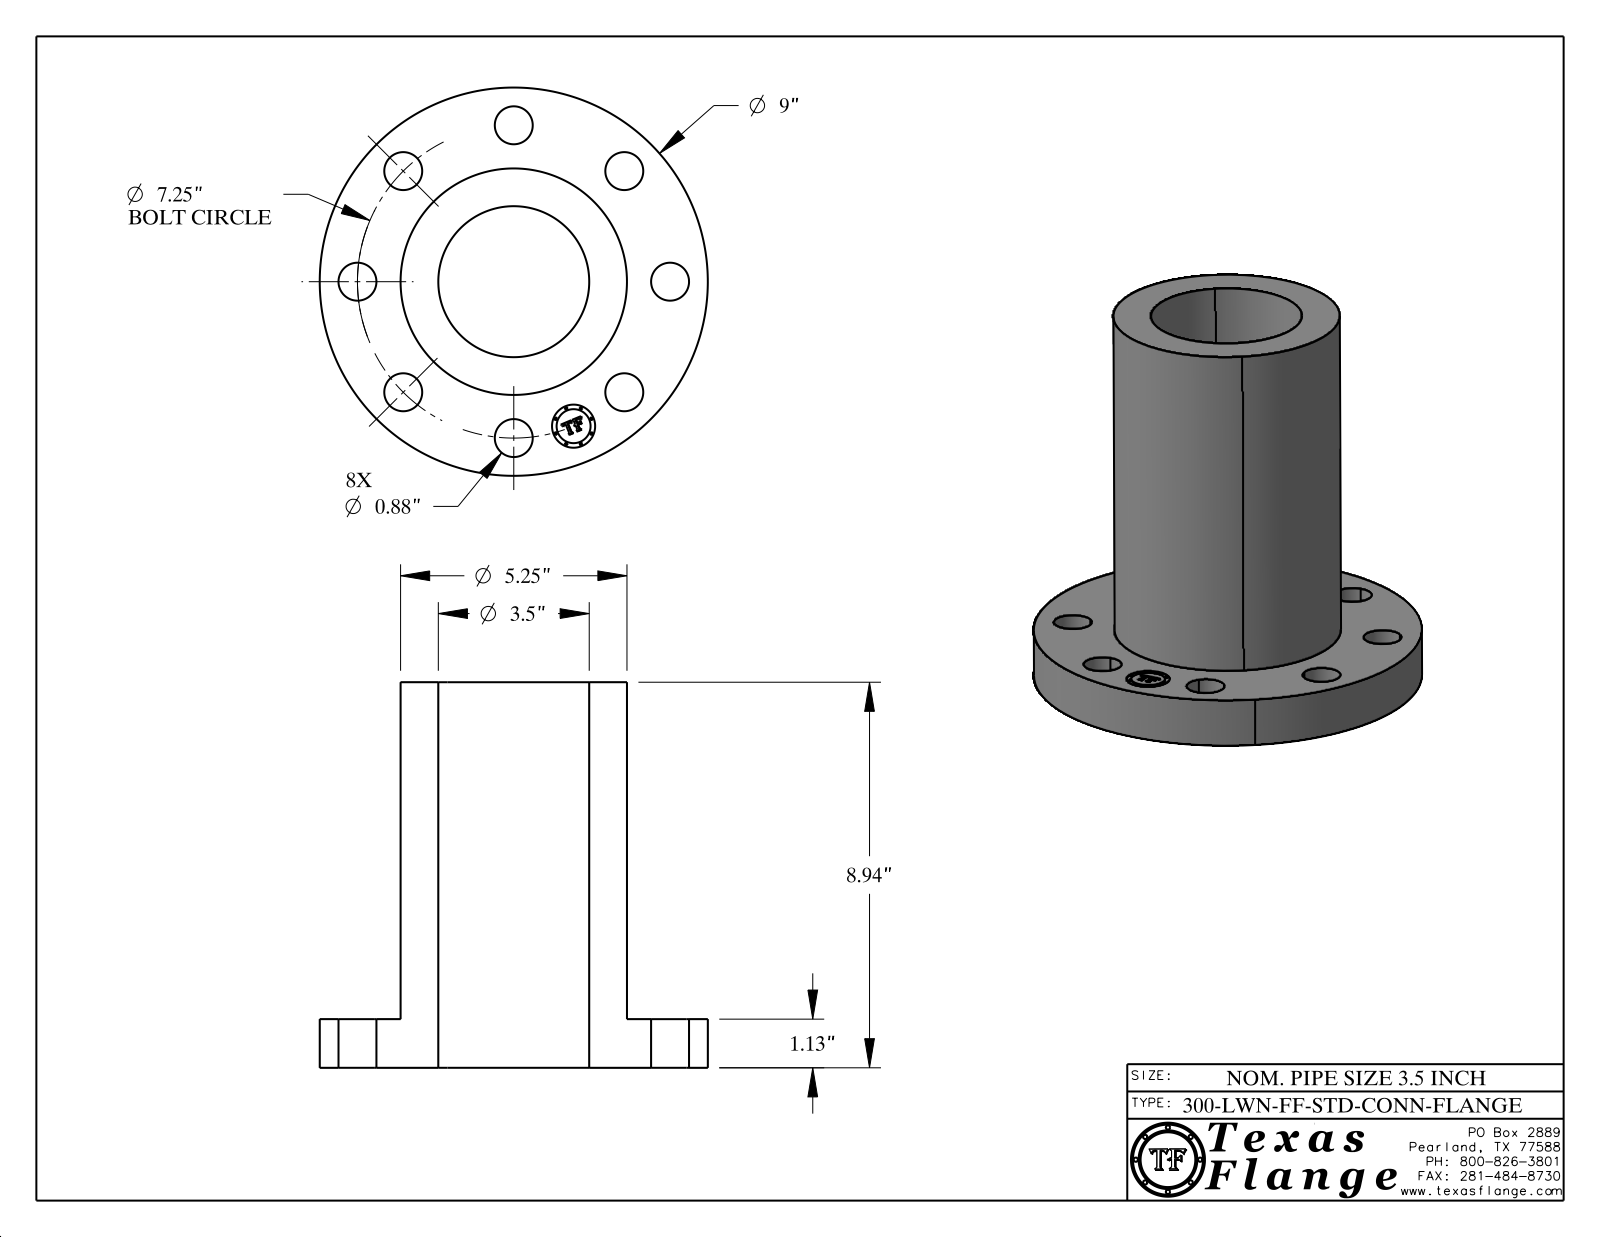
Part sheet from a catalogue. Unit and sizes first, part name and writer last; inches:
Units: inches
Overall size (bounding box): 9 × 9 × 8.938
Round holes (diameter × count): ⌀0.88 ×8, ⌀1 ×1, ⌀3.5 ×1
Round bosses / shafts (diameter × count): ⌀0.061 ×8, ⌀9 ×1, ⌀5.25 ×1, ⌀0.788 ×1
Main face-to-face distances: 1.128, 8.937, 7.81, 1.122, 7.815, 0.298, 0.292, 0.054, 0.193, 0.248
Hole centre spacings: 3.625, 2.774, 5.127, 6.698, 7.25, 1.415, 7.111, 4.028
Volume: 149.3 in³ · Surface area: 382.2 in²
Bodies: 1 solid, 410 faces (368 planar, 42 cylindrical, 0 other)
Part name (STEP PRODUCT): 3.5-300-LWN-FF-STD-CONN-FLANGE
STEP written by: CATIA V5 STEP AP214 (AUTOMOTIVE_DESIGN)
